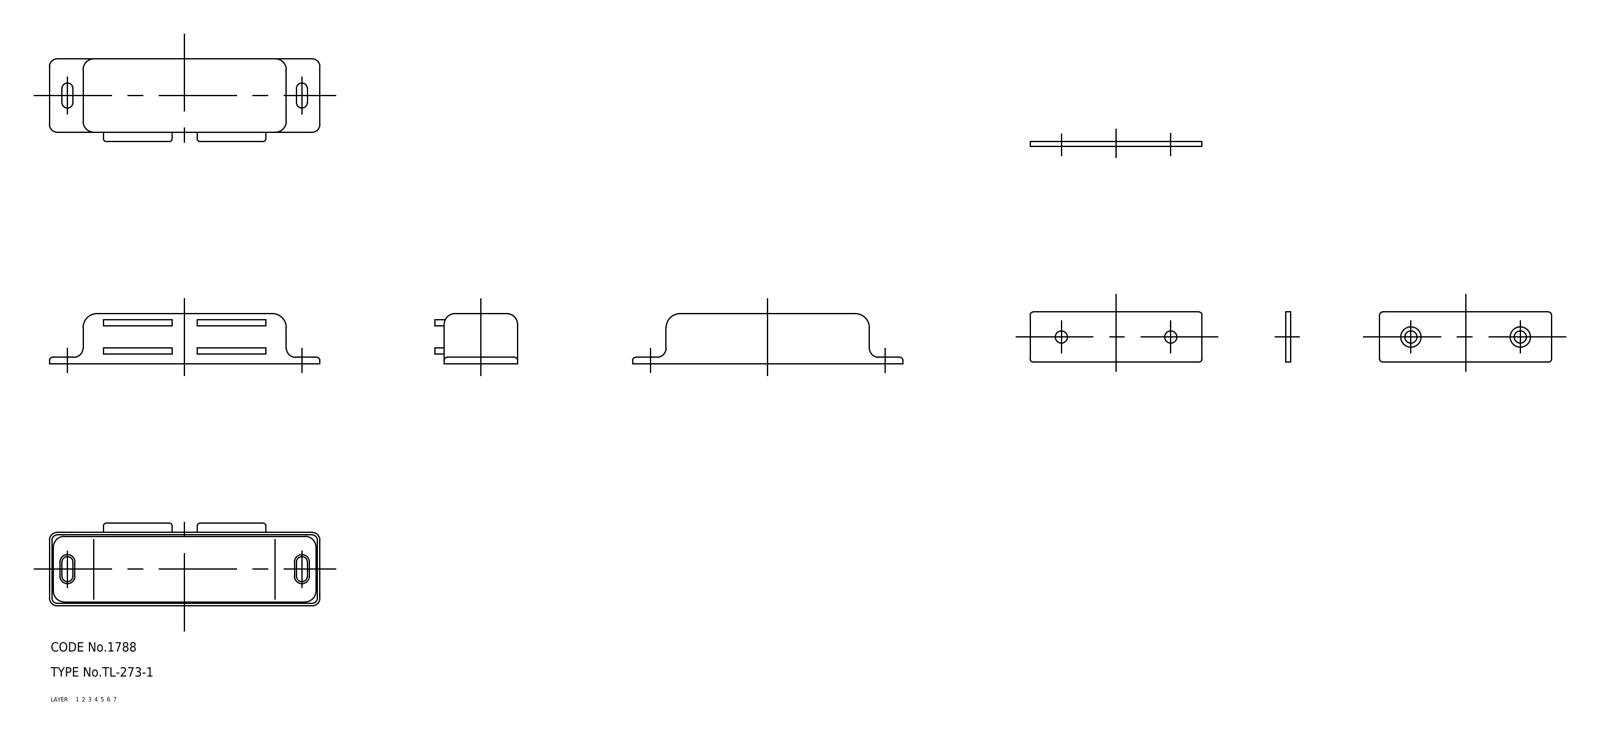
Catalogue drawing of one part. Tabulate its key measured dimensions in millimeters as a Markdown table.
| quantity | value |
| --- | --- |
| part name | attachment; keeper; housing; base (+1 more) |
| STEP written by | CADfix (AUTOMOTIVE_DESIGN) |
| units | millimeters |
| bodies | 7 solids, 183 faces (0 planar, 0 cylindrical, 183 other) |
| overall size | 86.5 × 53.1 × 16.5 |
| volume | 10 706 mm³ |
| surface area | 19 271 mm² |
